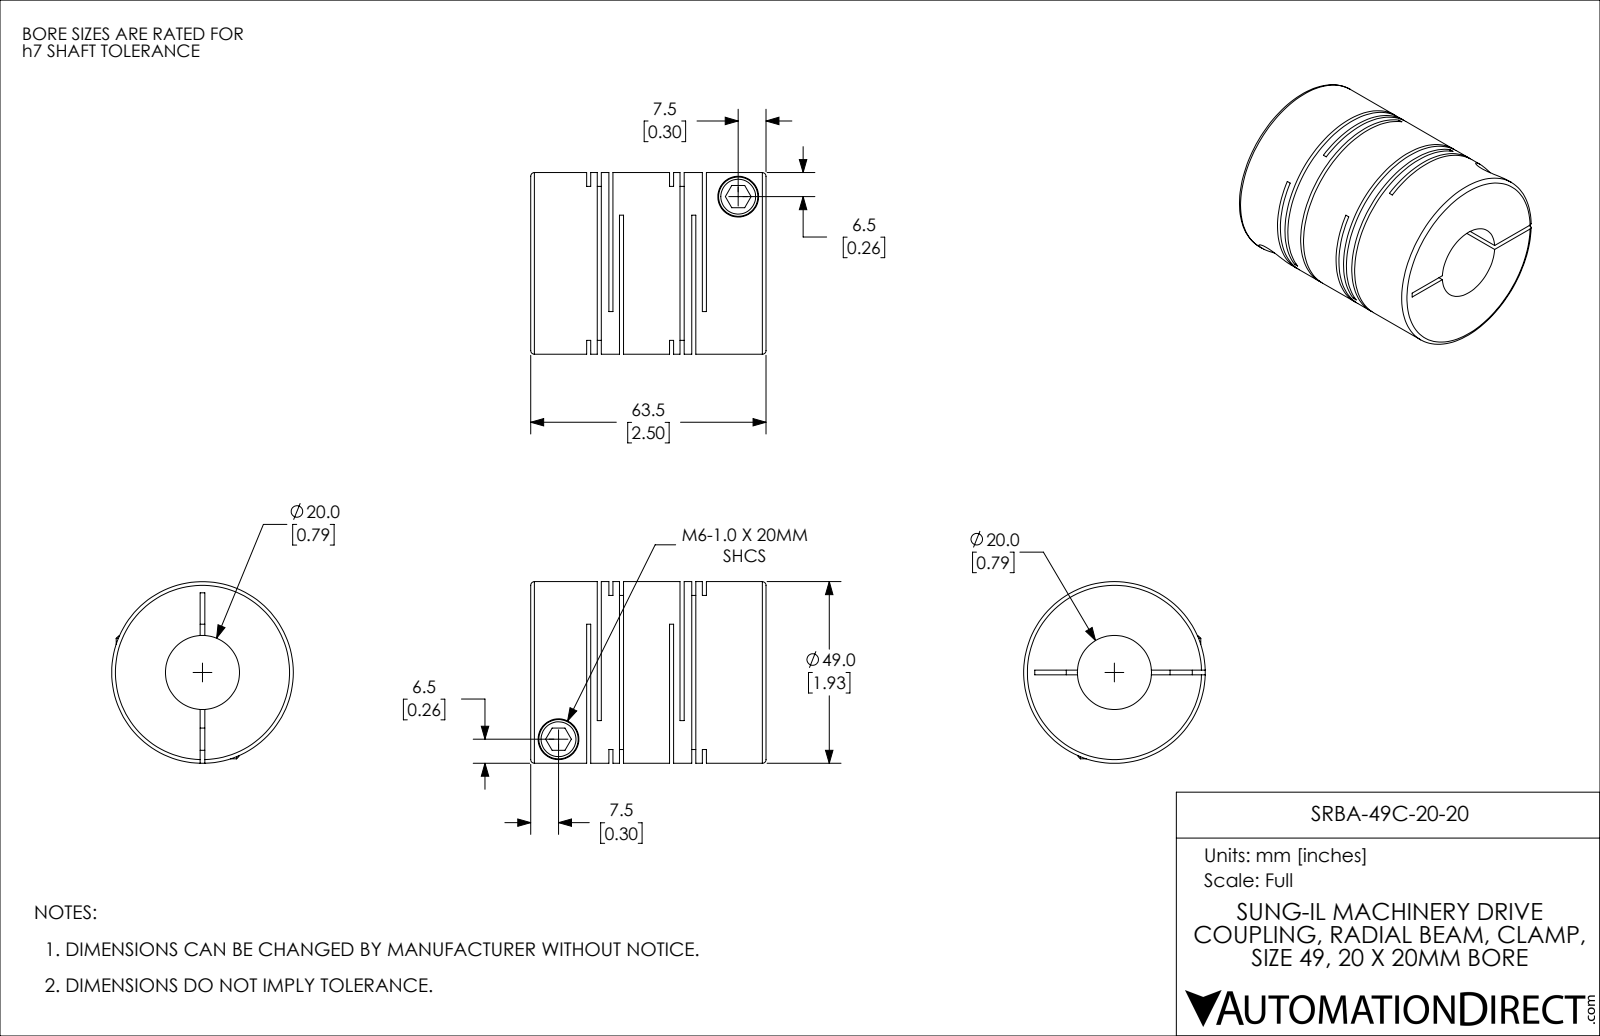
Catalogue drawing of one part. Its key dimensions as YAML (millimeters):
part_name: "SRBA-49C-20-20"
step_written_by: "SolidWorks 2021 (CONFIG_CONTROL_DESIGN)"
units: millimeters
bodies: {solids: 1, faces: 114, planar: 60, cylindrical: 42, other: 12}
overall_size: [63.5, 49, 49]
volume: 86229
surface_area: 37968
round_holes:
  - {diameter: 6, count: 2}
  - {diameter: 11, count: 2}
  - {diameter: 20, count: 1}
round_bosses_or_shafts:
  - {diameter: 10.6, count: 2}
  - {diameter: 49, count: 1}
face_to_face_distances: [6, 1.1, 2.85, 22.35, 1.75, 4.9, 21.25, 3.15, 19.5, 16.35]
